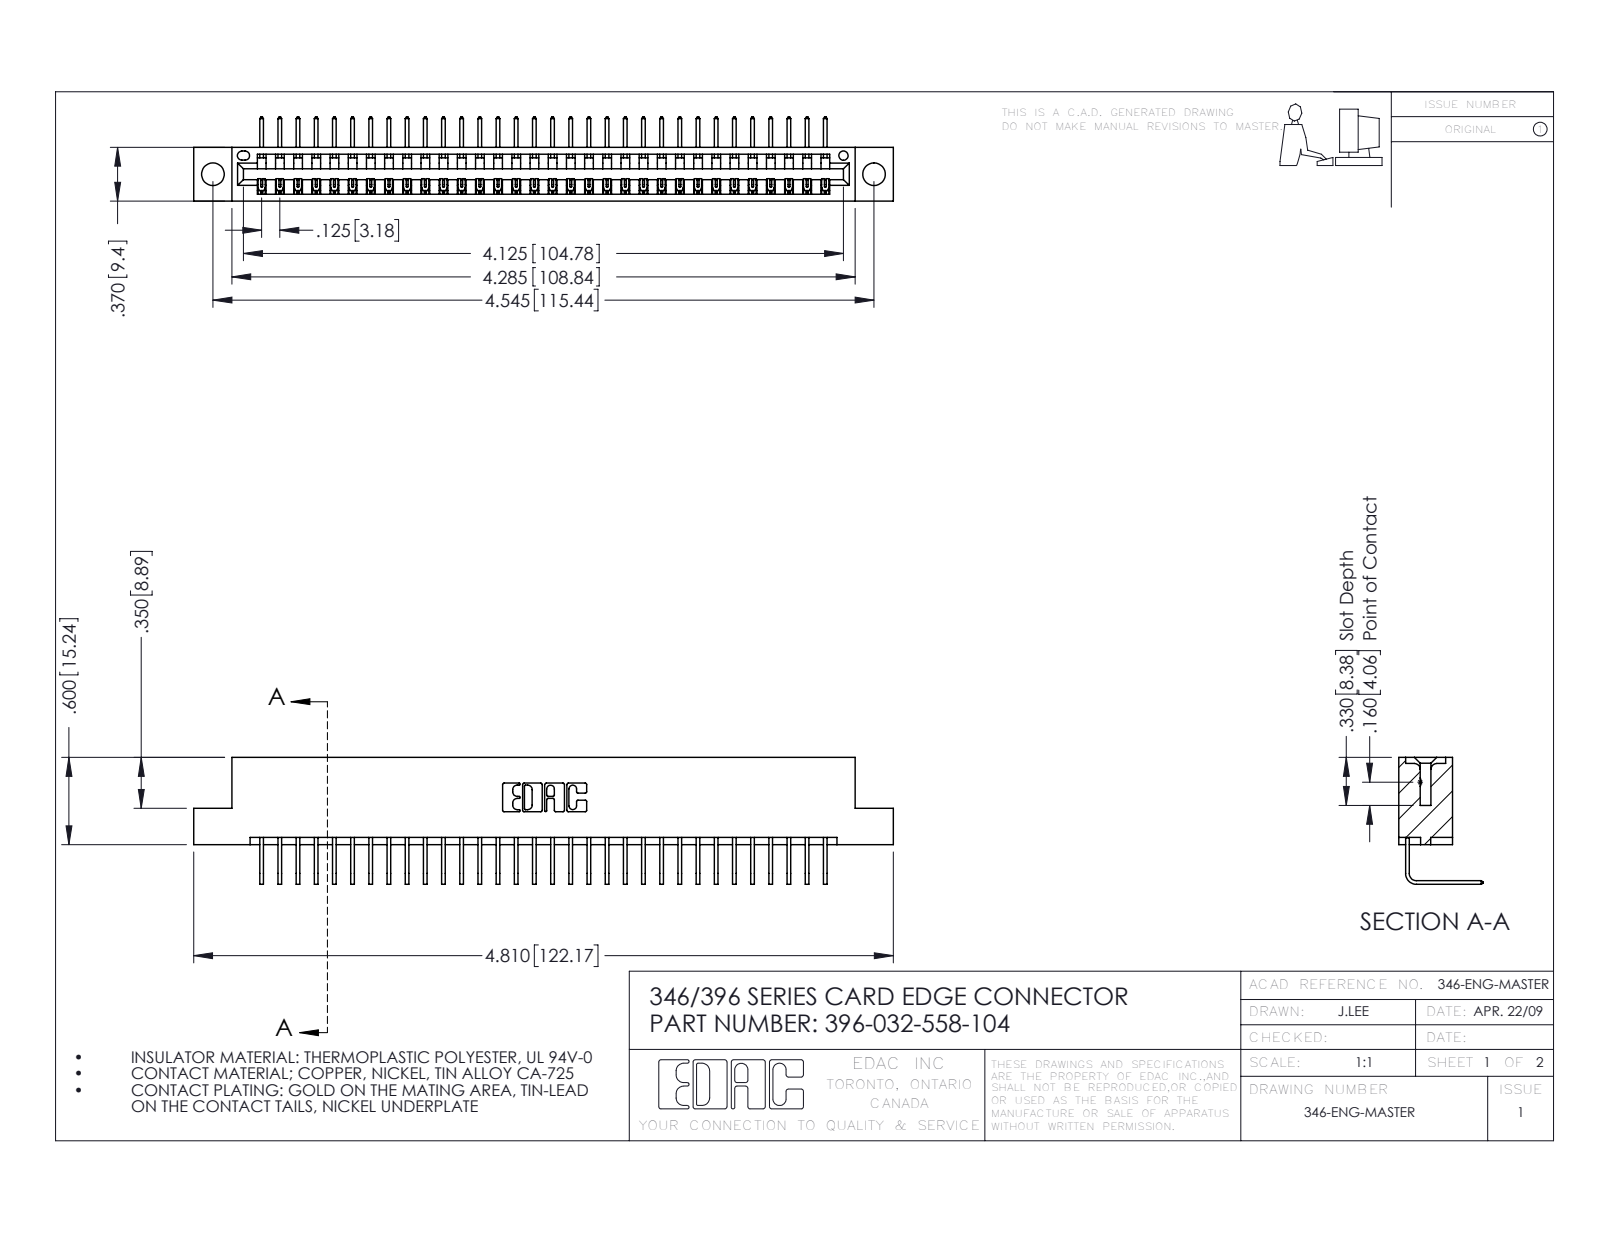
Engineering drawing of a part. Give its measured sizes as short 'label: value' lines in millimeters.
name: 345-292-001_558 Tail - 2; 346 Part_Flush Mounting Lugs - 0.156 Dia-TH; 396-032-558-104
written by: SolidWorks 2016 (CONFIG_CONTROL_DESIGN)
unit: mm
bodies: 33 solids, 2042 faces (1420 planar, 622 cylindrical, 0 other)
size: 122.2 × 22.2 × 14.7
volume: 11 700 mm³; area: 14 890 mm²
holes: 2× ⌀4, 1× ⌀1.6
rounds: 64× R0.2, 22× R0.3, 6× R0.2, 6× R0.8, 3× R0.7, 2× R0.8, 2× R1, 1× R0.4
face distances: 8.2, 1.2, 9.4, 6.4, 7.6, 0.6, 1.8, 3.8, 5.6, 2.5
hole spacings: 6.2, 110.2, 115.4
